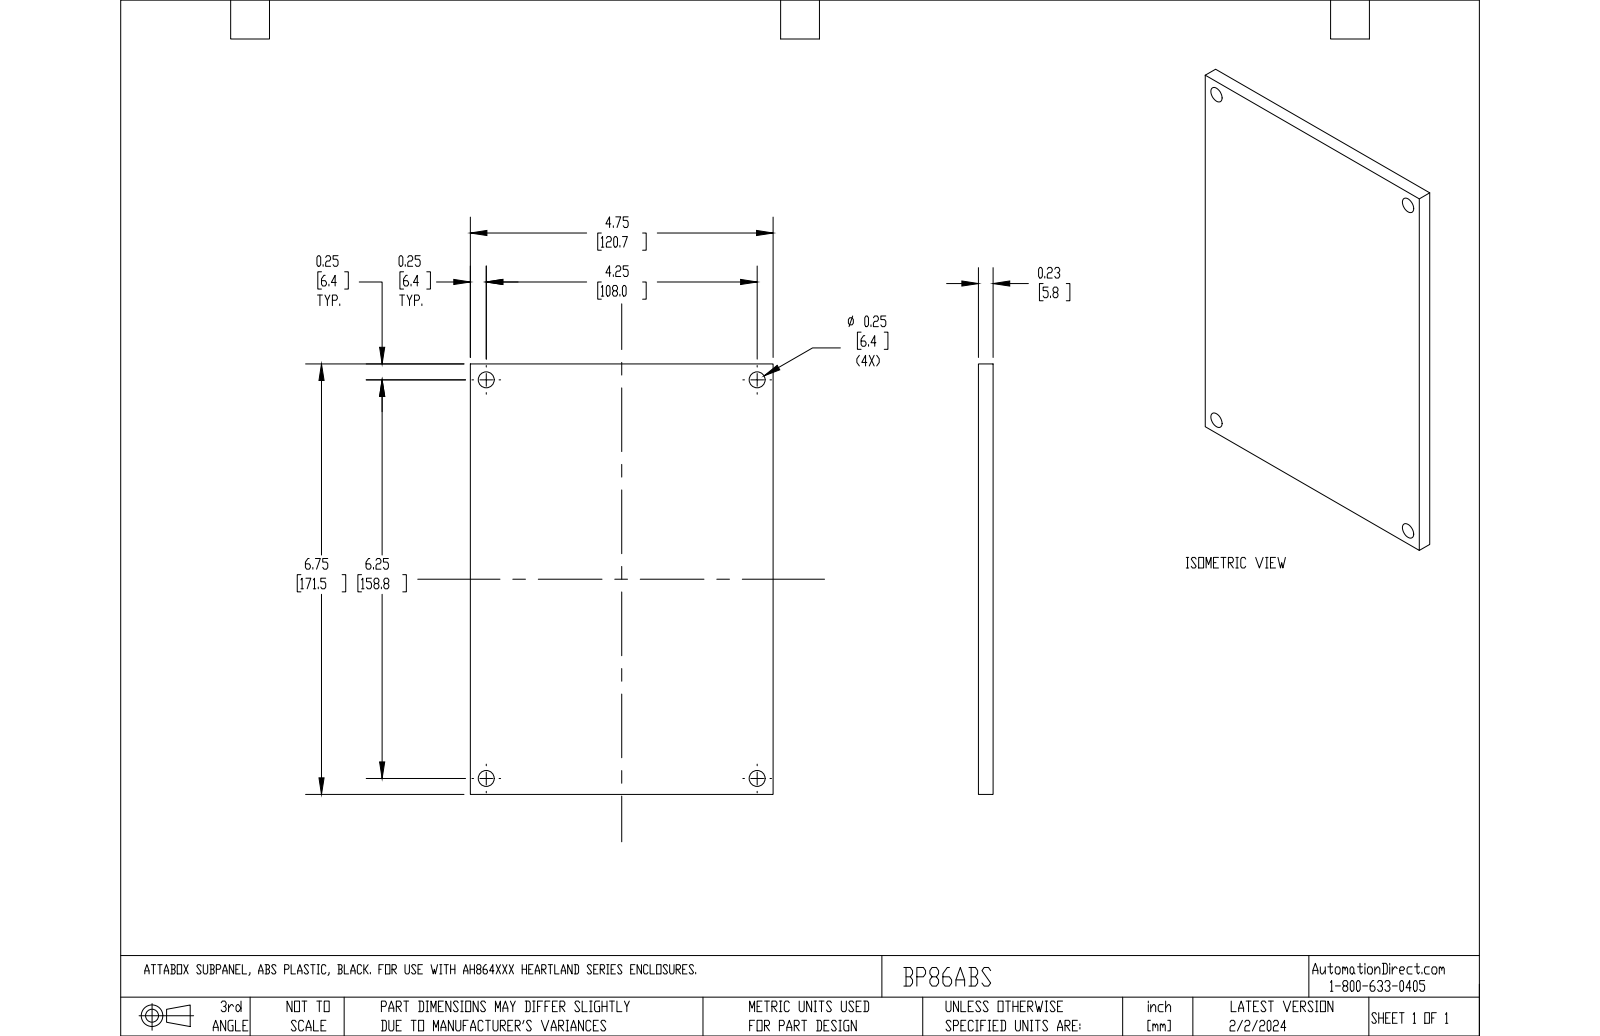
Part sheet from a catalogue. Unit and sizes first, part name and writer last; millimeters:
Units: millimetres
Overall size (bounding box): 171.45 × 120.65 × 5.84
Round holes (diameter × count): ⌀6.35 ×4
Main face-to-face distances: 5.84, 120.64, 171.44
Hole centre spacings: 107.94, 158.76, 191.98
Volume: 120 104 mm³ · Surface area: 44 997 mm²
Bodies: 1 solid, 10 faces (6 planar, 4 cylindrical, 0 other)
Part name (STEP PRODUCT): ATBP86ABS
STEP written by: Autodesk Inventor 2017 (AUTOMOTIVE_DESIGN)
